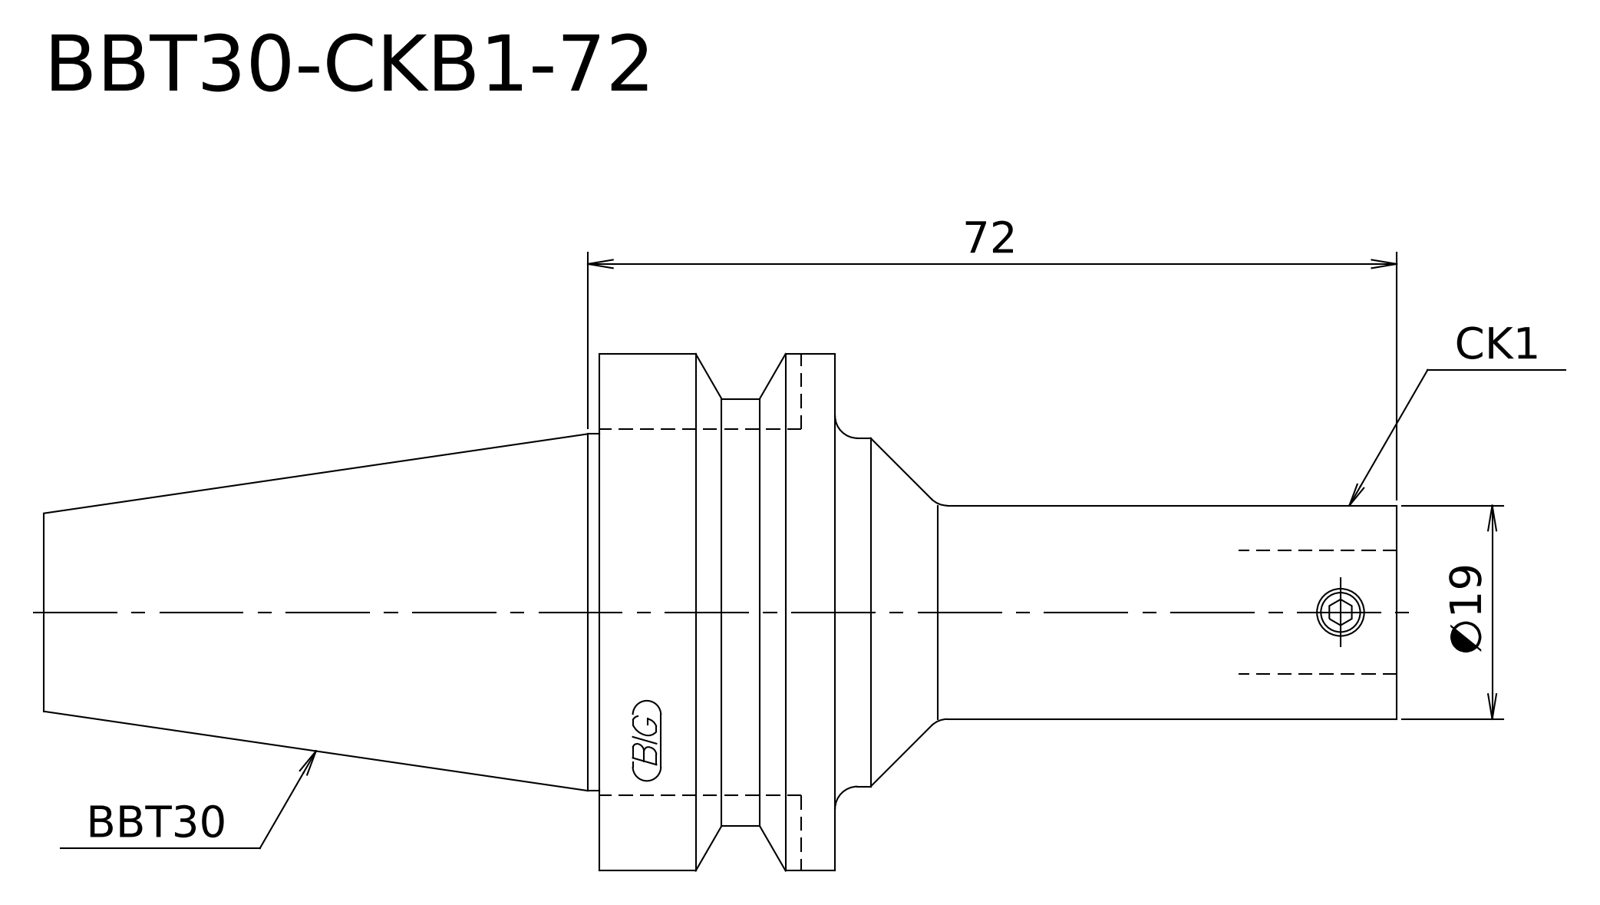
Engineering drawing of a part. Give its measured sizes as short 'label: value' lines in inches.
written by: Kubotek KeyCreator V8.5.1 (14335) (CONFIG_CONTROL_DESIGN)
unit: in
bodies: 1 solid, 16 faces (4 planar, 6 cylindrical, 6 other)
size: 4.74 × 1.811 × 1.811
volume: 4.518 in³; area: 20.19 in²
bosses: 1× ⌀1.811, 1× ⌀1.496, 1× ⌀1.25, 1× ⌀1.22, 1× ⌀0.748
face distances: 0.827, 1.969, 2.795, 4.74, 2.772, 1.945
